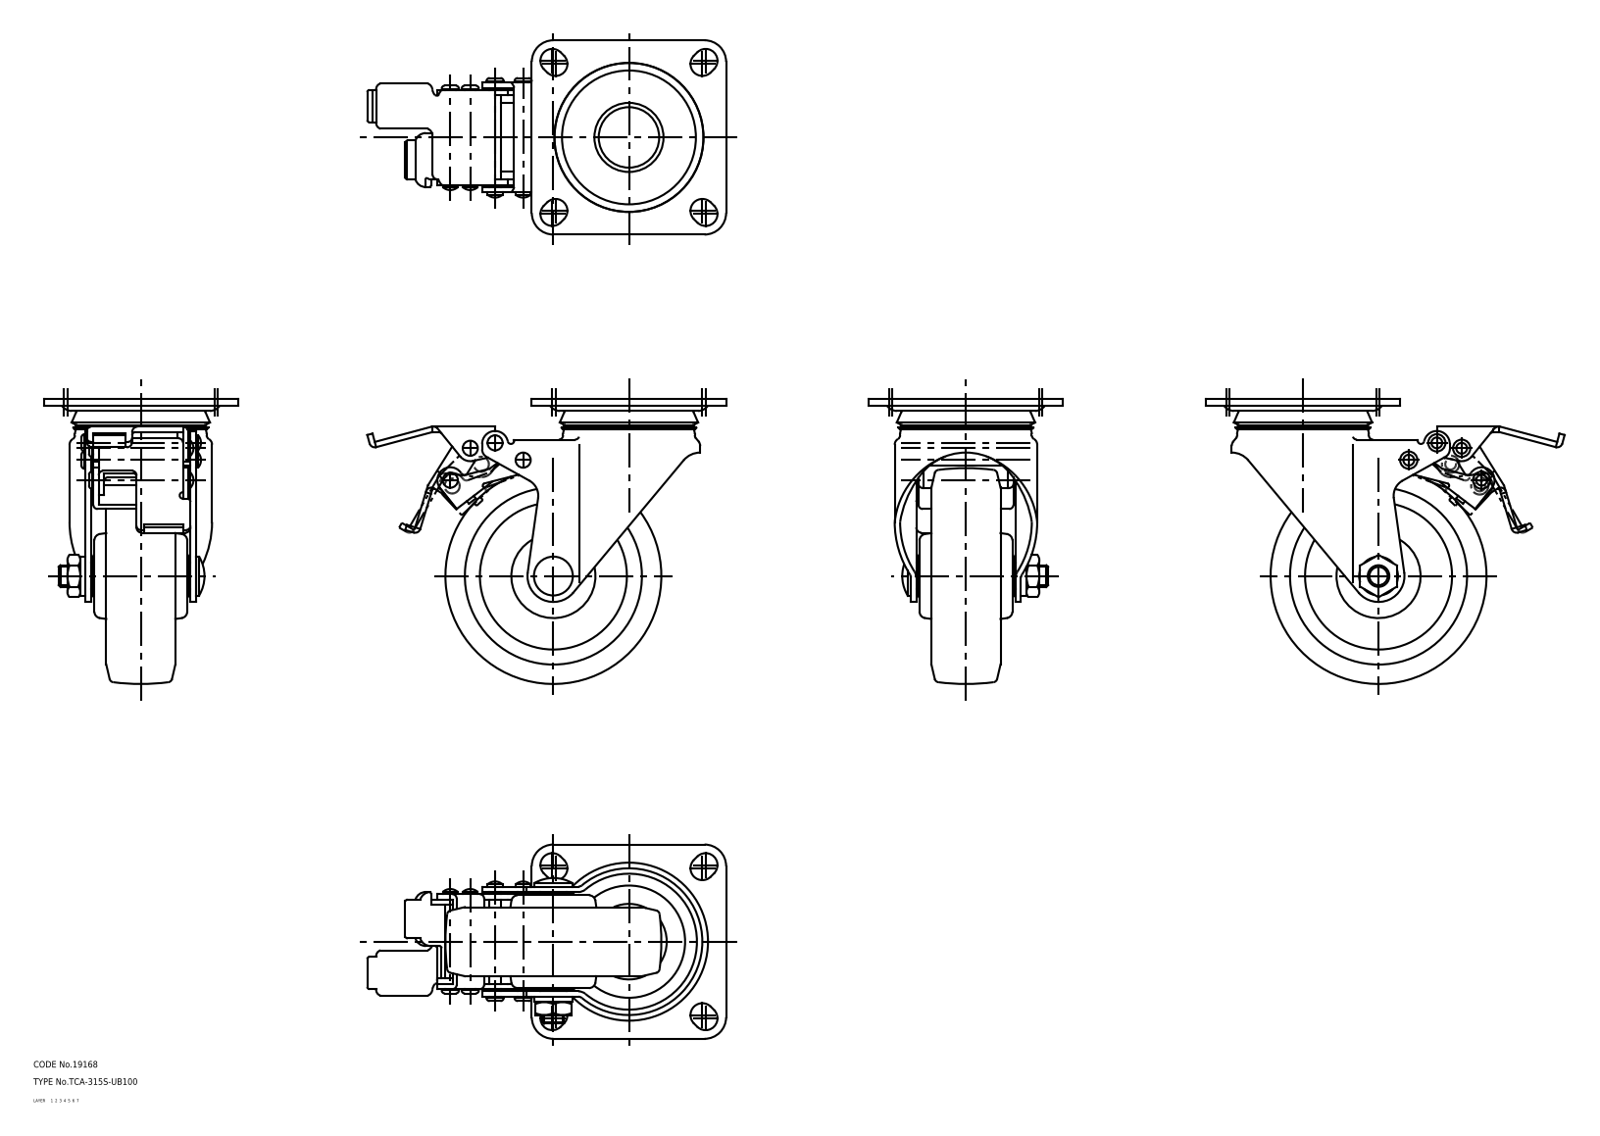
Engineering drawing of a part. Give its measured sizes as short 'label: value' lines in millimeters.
name: wheel; mounting plate; main shaft; lever (+2 more)
written by: CADfix (AUTOMOTIVE_DESIGN)
unit: mm
bodies: 6 solids, 450 faces (0 planar, 0 cylindrical, 450 other)
size: 166.18 × 132 × 90
volume: 354 783 mm³; area: 100 238 mm²
